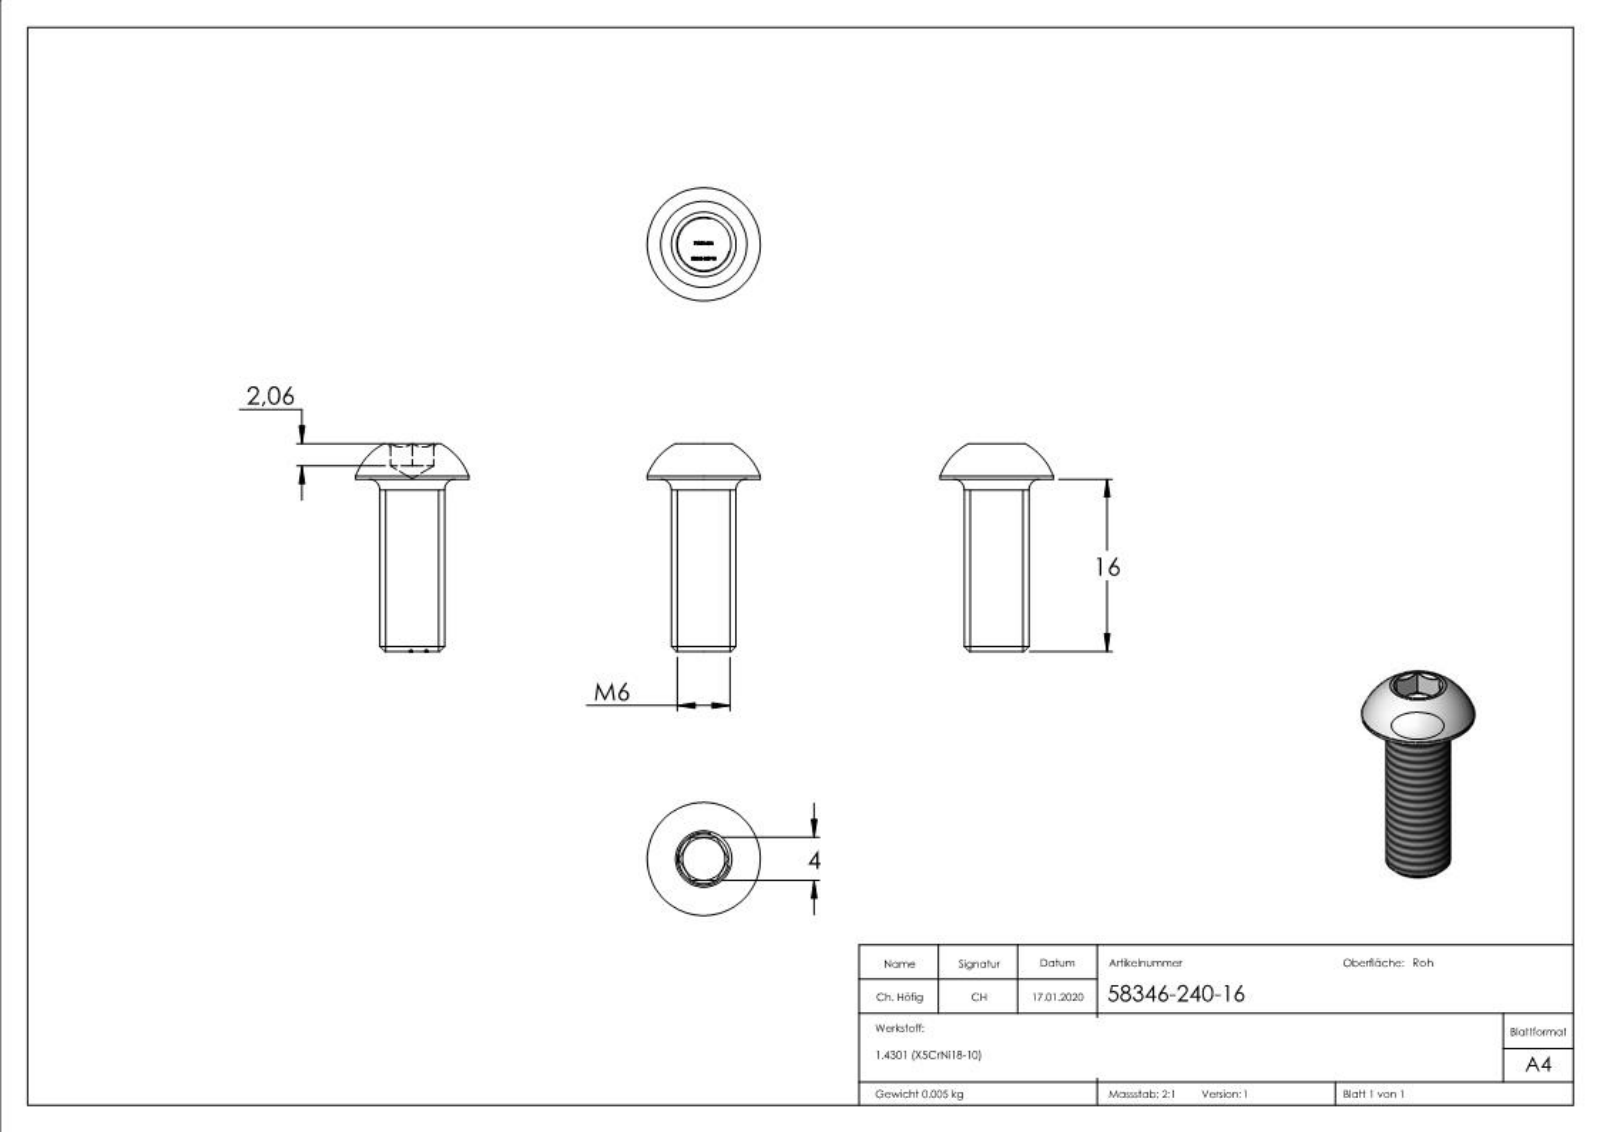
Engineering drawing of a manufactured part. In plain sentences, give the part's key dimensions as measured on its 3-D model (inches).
The part is named "58346-240-16". Its 3-D file was written by "SolidWorks 2015 (CONFIG_CONTROL_DESIGN)". It is 1 solid with 287 faces: 155 planar, 2 cylindrical and 130 other. Overall it measures 0.839 by 0.413 by 0.413 inches. Its volume is 0.038 cubic inches and its surface area 0.842 square inches. Round bosses or shafts: 1 of diameter 0.413, 1 of diameter 0.236. The main face-to-face distances are 0.63, 0.157, 0.13, 0.76, 0.049, 0.081, 0.679, 0.756, 0.675, 0.626.
